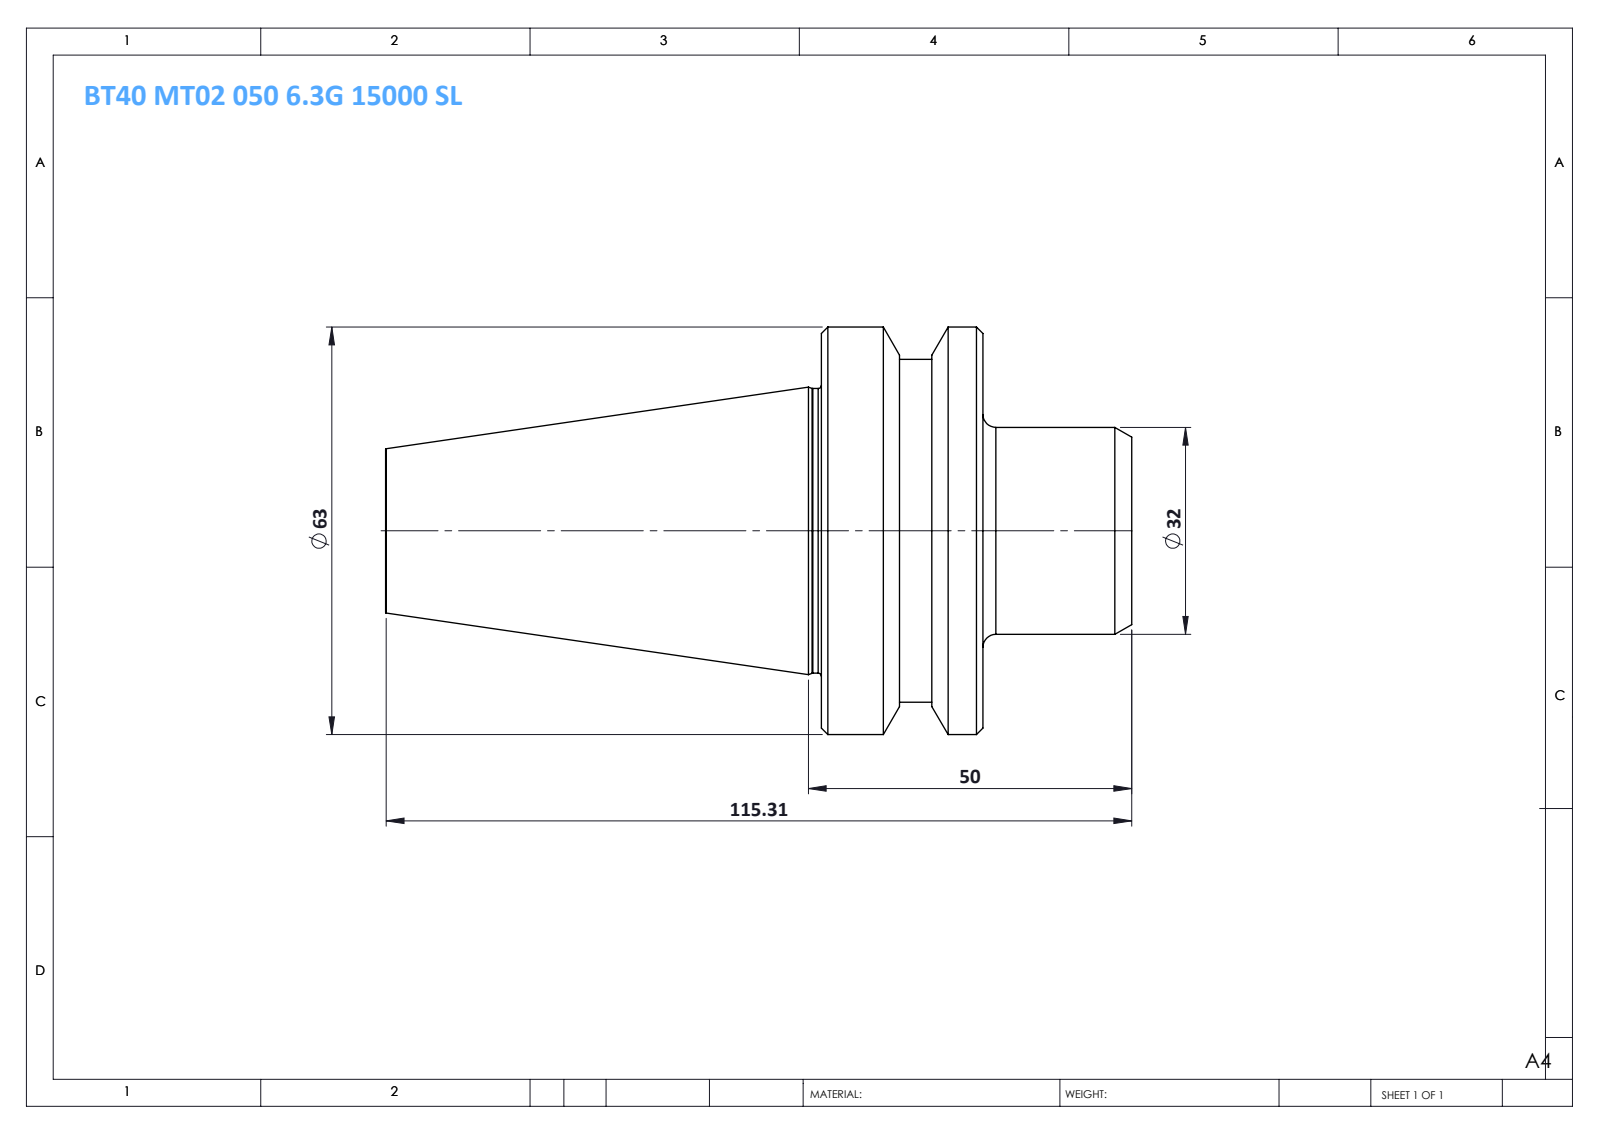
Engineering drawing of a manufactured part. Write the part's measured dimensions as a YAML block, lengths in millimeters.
part_name: "BT40 MT02 050 6.3G 15000 SL"
step_written_by: "SolidWorks 2014 (CONFIG_CONTROL_DESIGN)"
units: millimeters
bodies: {solids: 1, faces: 38, planar: 6, cylindrical: 10, other: 22}
overall_size: [115.4, 63, 63]
volume: 156762
surface_area: 20464
round_bosses_or_shafts:
  - {diameter: 63, count: 1}
  - {diameter: 53, count: 1}
  - {diameter: 44, count: 1}
  - {diameter: 32, count: 1}
face_to_face_distances: [25, 23, 48, 115.4, 92.4, 67.4, 35.9, 12.9, 12.1, 79.5]
